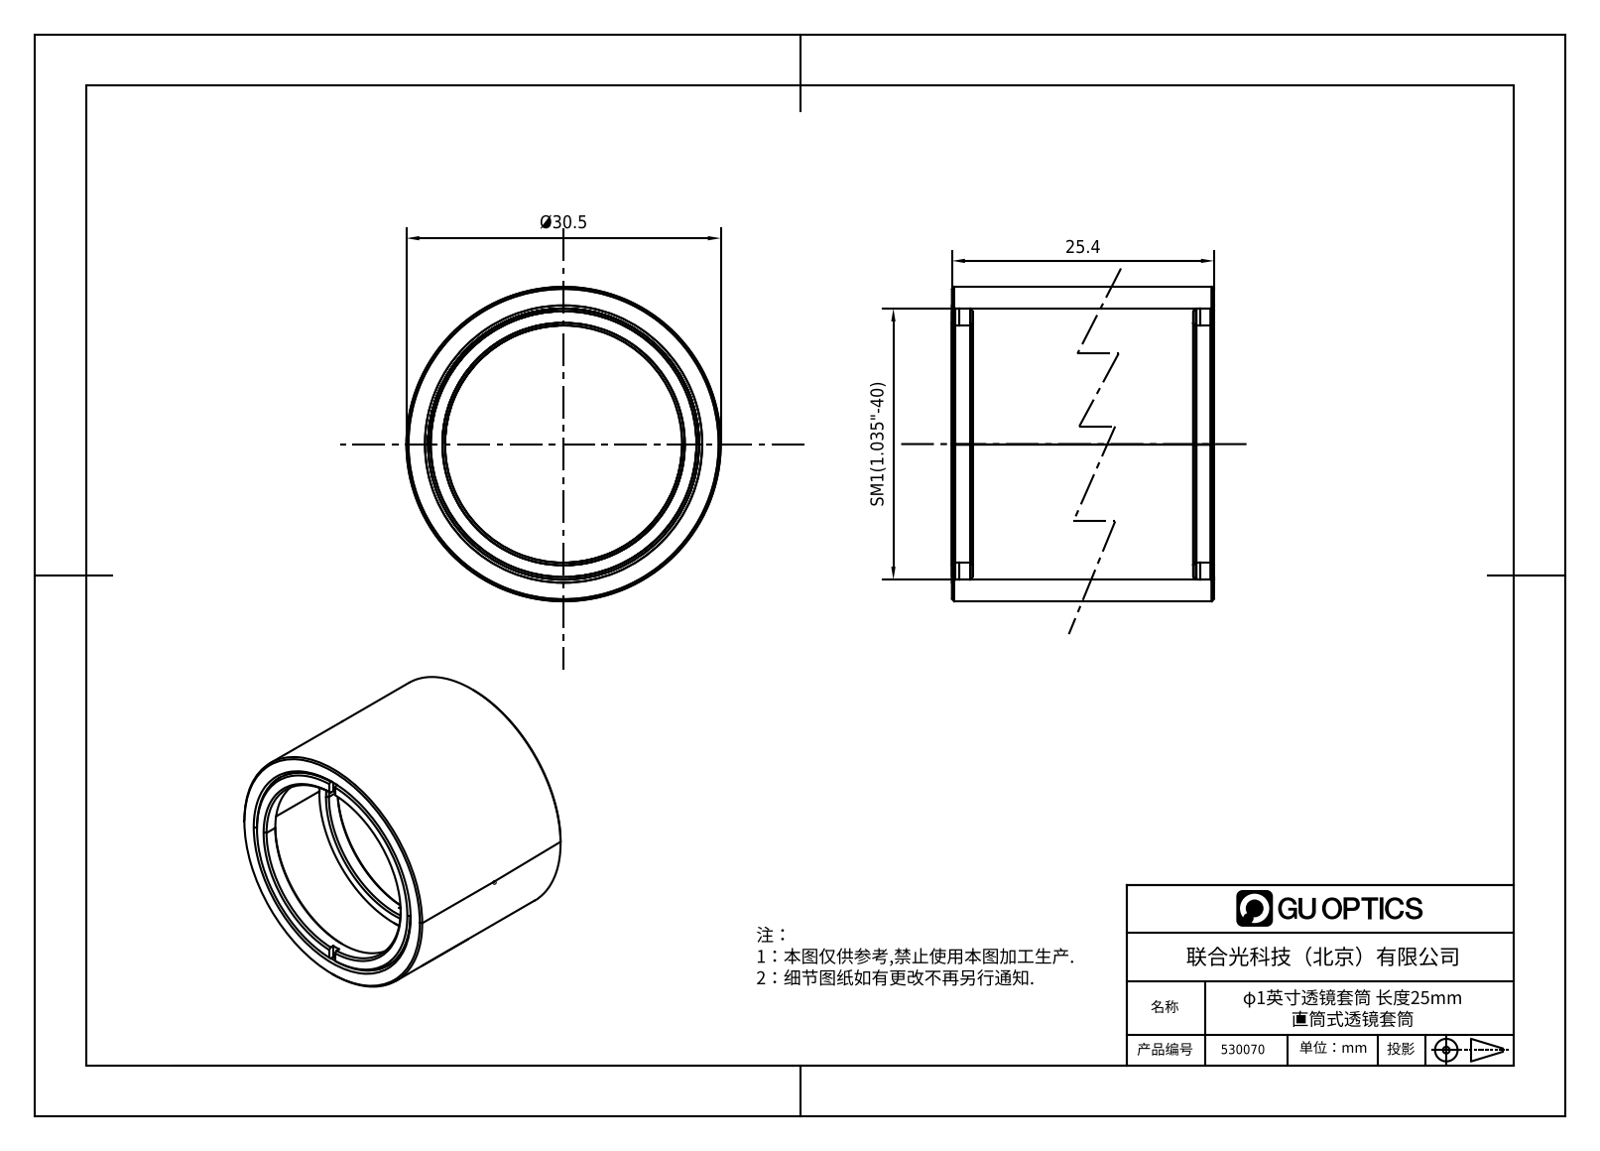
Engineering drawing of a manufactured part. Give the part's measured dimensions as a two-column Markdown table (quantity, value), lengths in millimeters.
| quantity | value |
| --- | --- |
| part name | 1.7.2.8_ZTZ-1-1.0_SM1标准型1.0英寸直筒式透镜套筒 |
| STEP written by | SolidWorks 2018 (AUTOMOTIVE_DESIGN) |
| units | millimeters |
| bodies | 0 solids, 54 faces (18 planar, 12 cylindrical, 24 other) |
| overall size | 30.5 × 30.5 × 25.4 |
| round holes (diameter × count) | 23.01 × 1, 26.3 × 1 |
| round bosses / shafts (diameter × count) | 30.5 × 1, 26.29 × 1 |
| main face-to-face distances | 25.4, 0.7, 24.7, 1, 24 |
